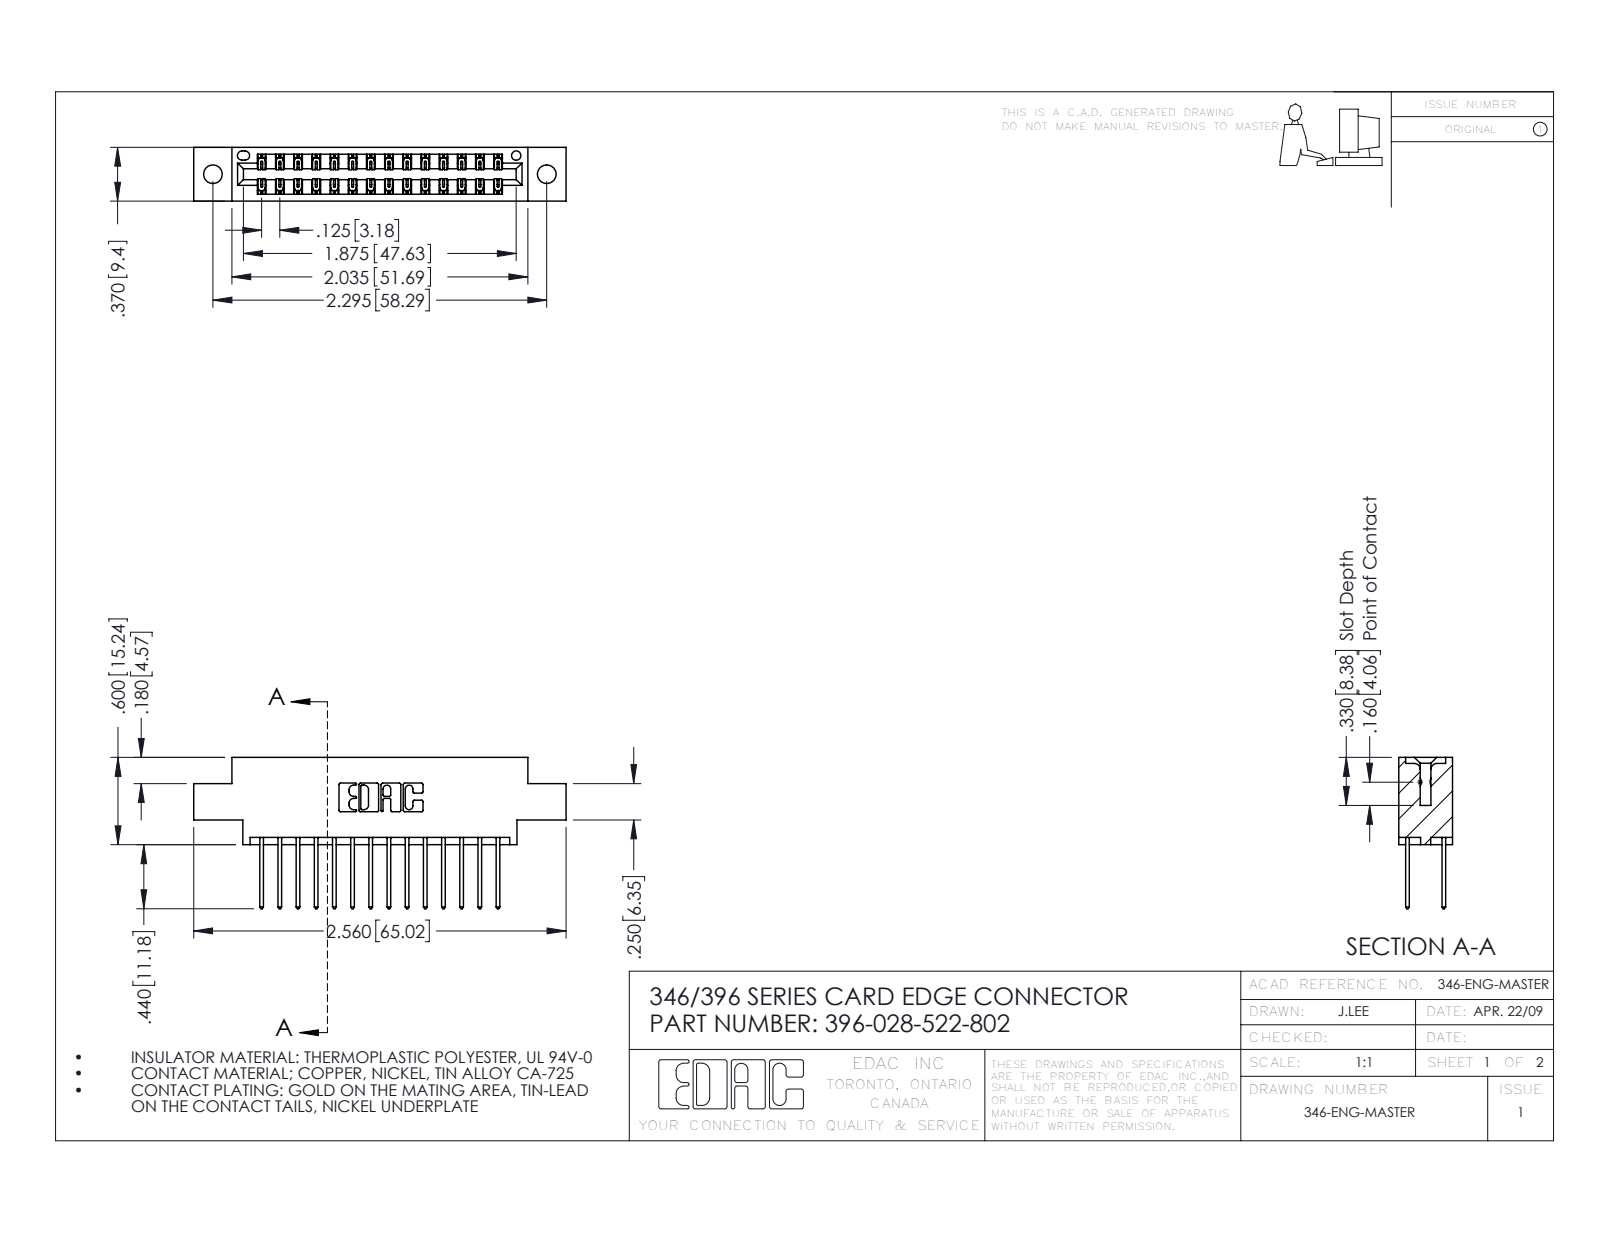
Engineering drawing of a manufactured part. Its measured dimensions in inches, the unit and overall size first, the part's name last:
Units: inches
Overall size (bounding box): 2.56 × 1.04 × 0.37
Round holes (diameter × count): ⌀0.128 ×2, ⌀0.064 ×1
Partial cylindrical surfaces — rounded edges, fillets, slot ends (radius × count): R0.006 ×42, R0.01 ×28, R0.01 ×22, R0.007 ×6, R0.031 ×6, R0.026 ×3, R0.014 ×2, R0.022 ×2
Main face-to-face distances: 0.048, 0.322, 0.25, 0.37, 0.072, 0.298, 0.025, 0.275, 0.148, 0.222
Hole centre spacings: 0.246, 2.089, 2.295
Volume: 0.366 in³ · Surface area: 12.49 in²
Bodies: 29 solids, 1582 faces (1060 planar, 522 cylindrical, 0 other)
Part name (STEP PRODUCT): 346 Part_0.170 Offset - 0.128 Dia; 345-292-001_345-293-122; 396-028-522-802
STEP written by: SolidWorks 2016 (CONFIG_CONTROL_DESIGN)
